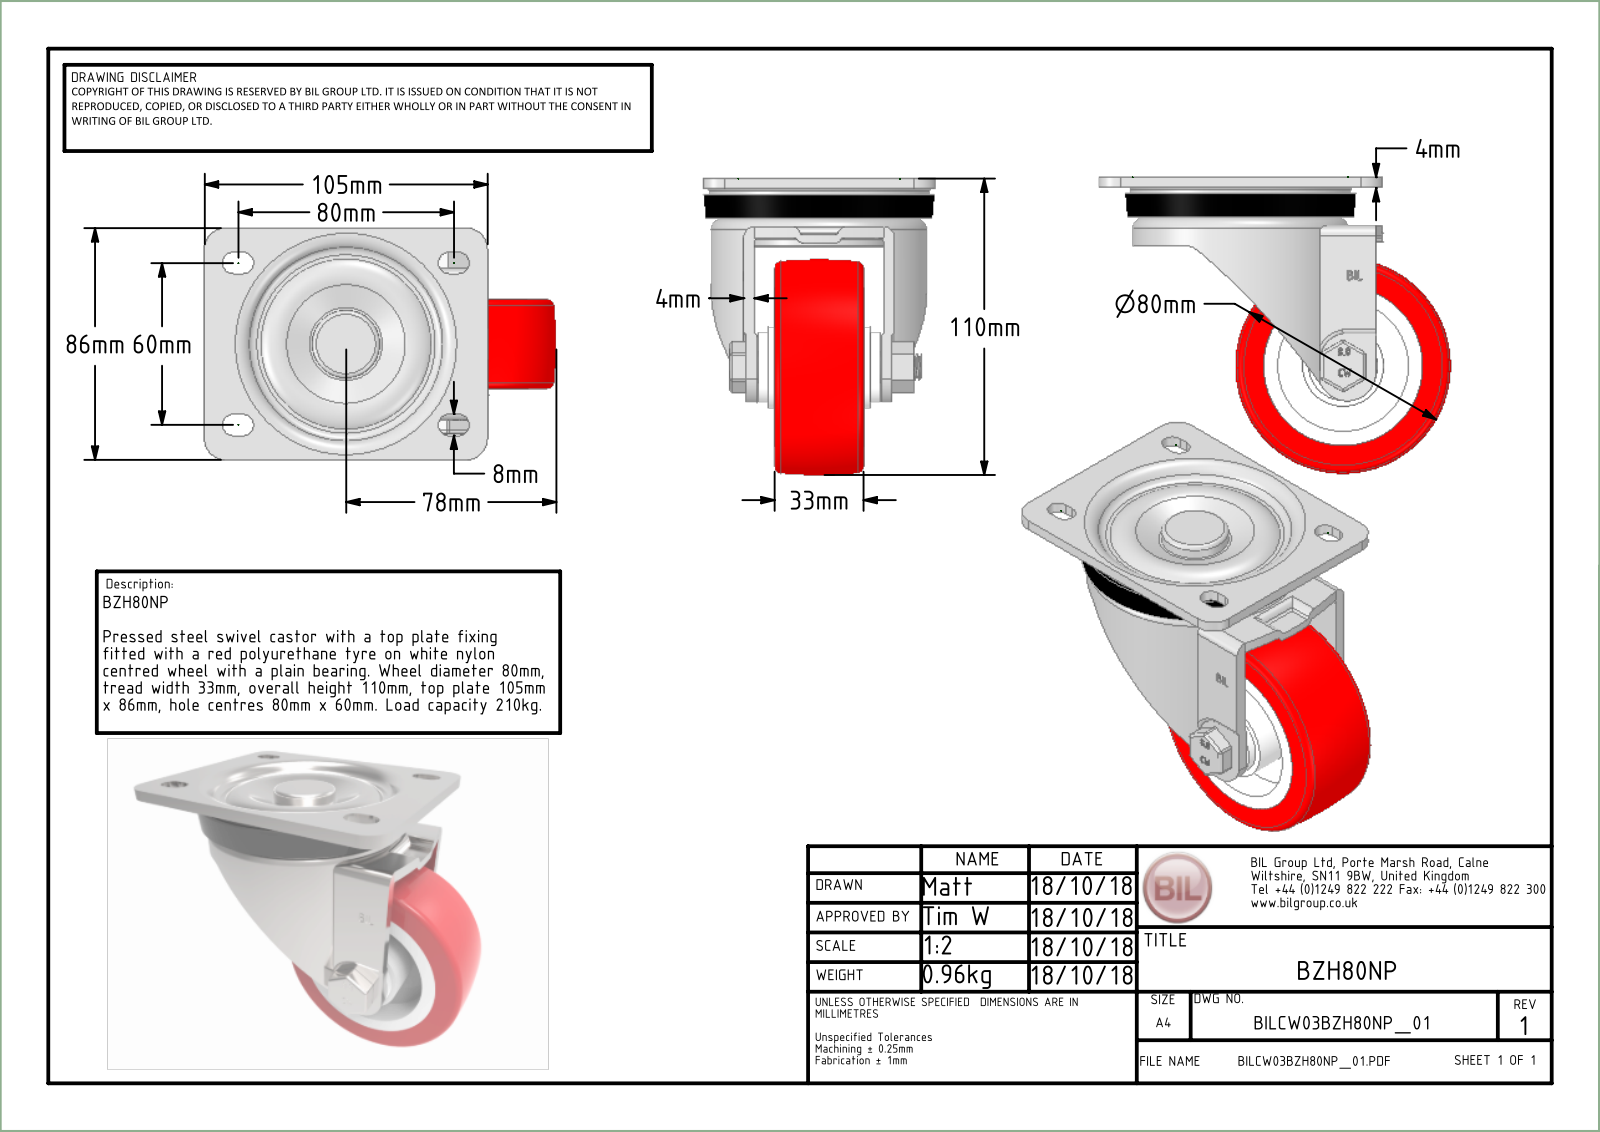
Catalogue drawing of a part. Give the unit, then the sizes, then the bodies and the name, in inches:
Units: inches
Overall size (bounding box): 5.138 × 4.331 × 3.386
Round holes (diameter × count): ⌀0.394 ×1, ⌀0.402 ×1, ⌀0.472 ×1, ⌀0.492 ×1, ⌀0.984 ×1, ⌀1.26 ×1, ⌀2.283 ×1, ⌀2.835 ×1
Round bosses / shafts (diameter × count): ⌀3.15 ×1, ⌀1.988 ×1, ⌀1.22 ×1, ⌀1.024 ×1, ⌀0.787 ×1, ⌀0.63 ×1, ⌀0.47 ×1, ⌀0.388 ×1
Partial cylindrical surfaces — rounded edges, fillets, slot ends (radius × count): R0.02 ×18, R0.177 ×8, R0.03 ×6, R0.079 ×4, R0.315 ×4, R0.157 ×2, R0.964 ×2, R0.517 ×1
Main face-to-face distances: 0.157, 0.413, 0.453, 0.295, 0.256, 0.787, 0.63, 0.768, 1.969, 1.713
Volume: 16.58 in³ · Surface area: 163.1 in²
Bodies: 9 solids, 387 faces (170 planar, 117 cylindrical, 100 other)
Part name (STEP PRODUCT): BZH80NP v4; BZH80AS - 2 v2; ZINC PLATED, PRESSED STEEL TOP PLATE; ZINC PLATED, PRESSED STEEL FORKS (+8 more)
STEP written by: Autodesk Translation Framework v14.10.0.0 (AUTOMOTIVE_DESIGN)
